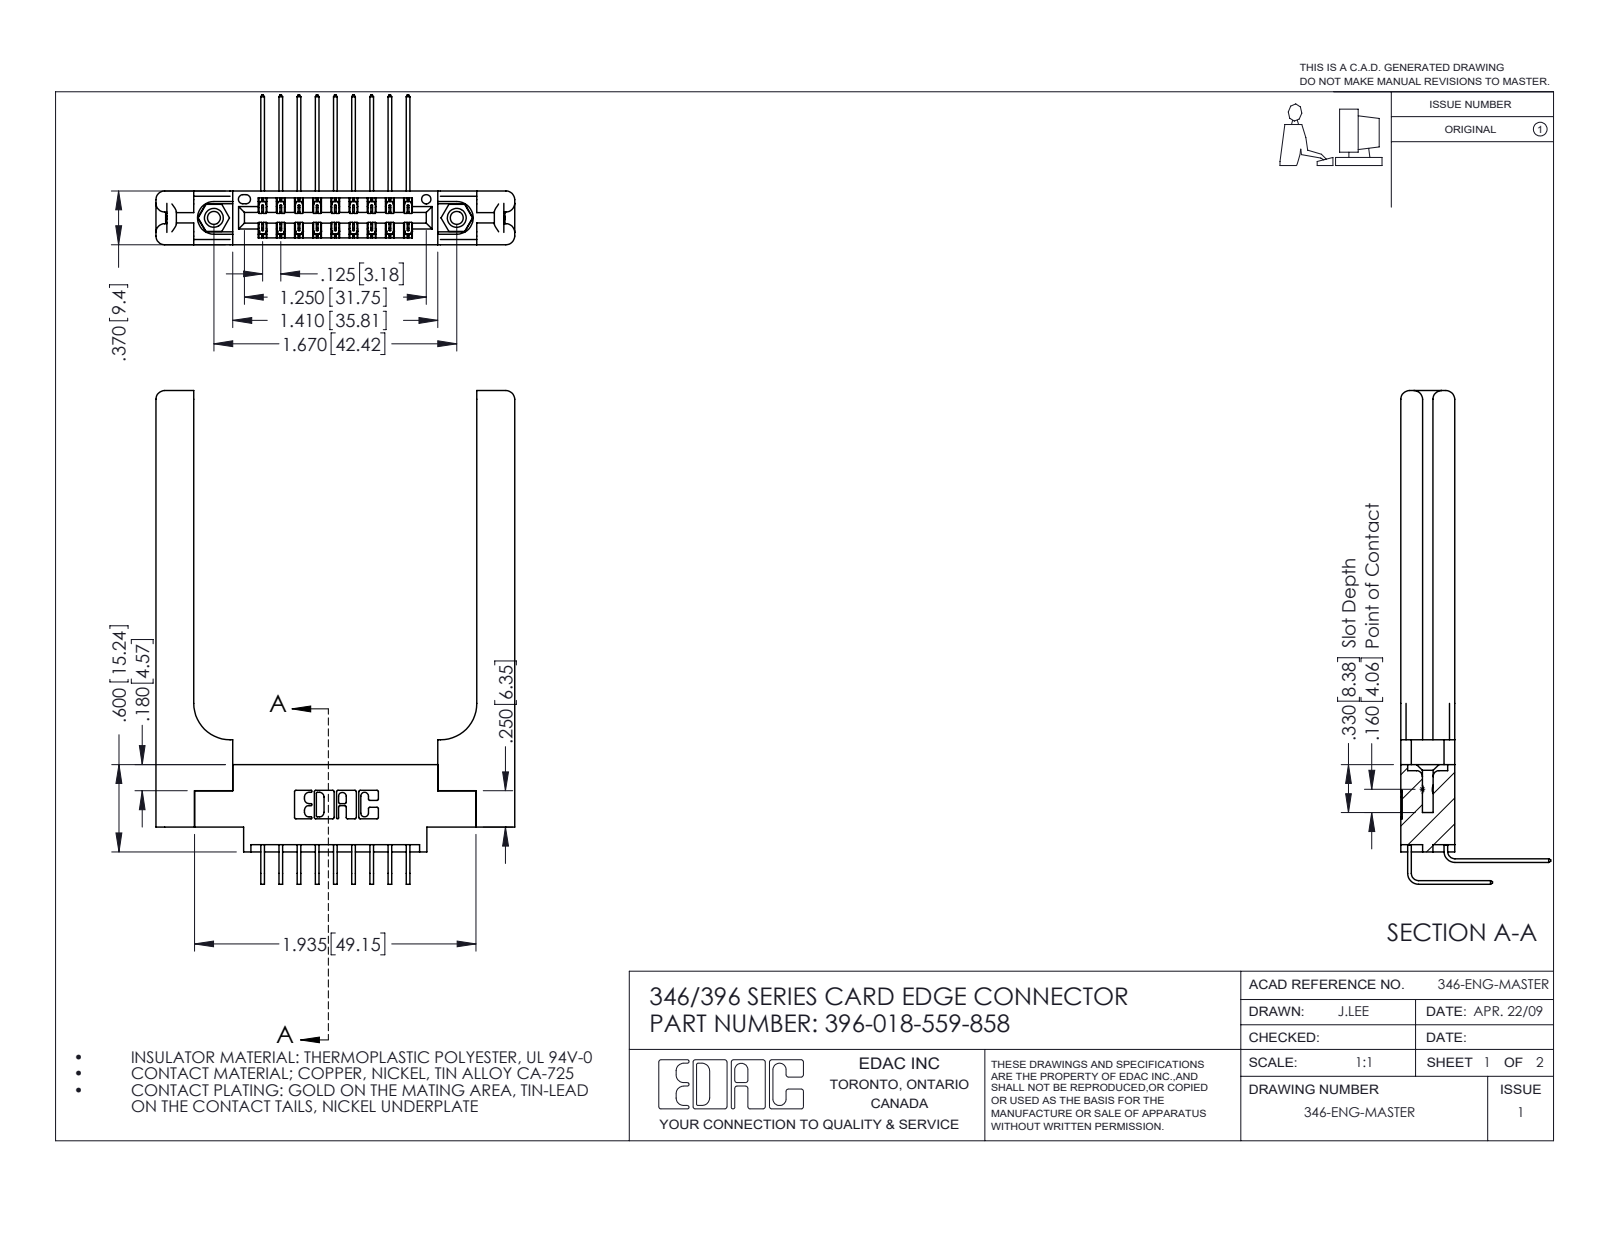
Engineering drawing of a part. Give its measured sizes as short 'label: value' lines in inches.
name: 345-292-001_559 Tail - 2; 346-220-058_345-220-058; 345-250-001_345-250-001-102; 346 Part_0.170 Offset - 0.156 Dia-TH (+2 more)
written by: SolidWorks 2016 (CONFIG_CONTROL_DESIGN)
unit: in
bodies: 23 solids, 1354 faces (894 planar, 400 cylindrical, 60 other)
size: 3.393 × 2.466 × 1.03
volume: 0.811 in³; area: 20.31 in²
holes: 2× ⌀0.089, 2× ⌀0.125, 2× ⌀0.156, 1× ⌀0.064
bosses: 2× ⌀0.155
rounds: 27× R0.006, 22× R0.01, 16× R0.06, 6× R0.007, 6× R0.031, 3× R0.026, 2× R0.014, 2× R0.022
face distances: 0.37, 0.15, 0.072, 0.22, 0.148, 0.048, 0.322, 0.102, 0.173, 0.25
hole spacings: 0.246, 1.465, 1.67
